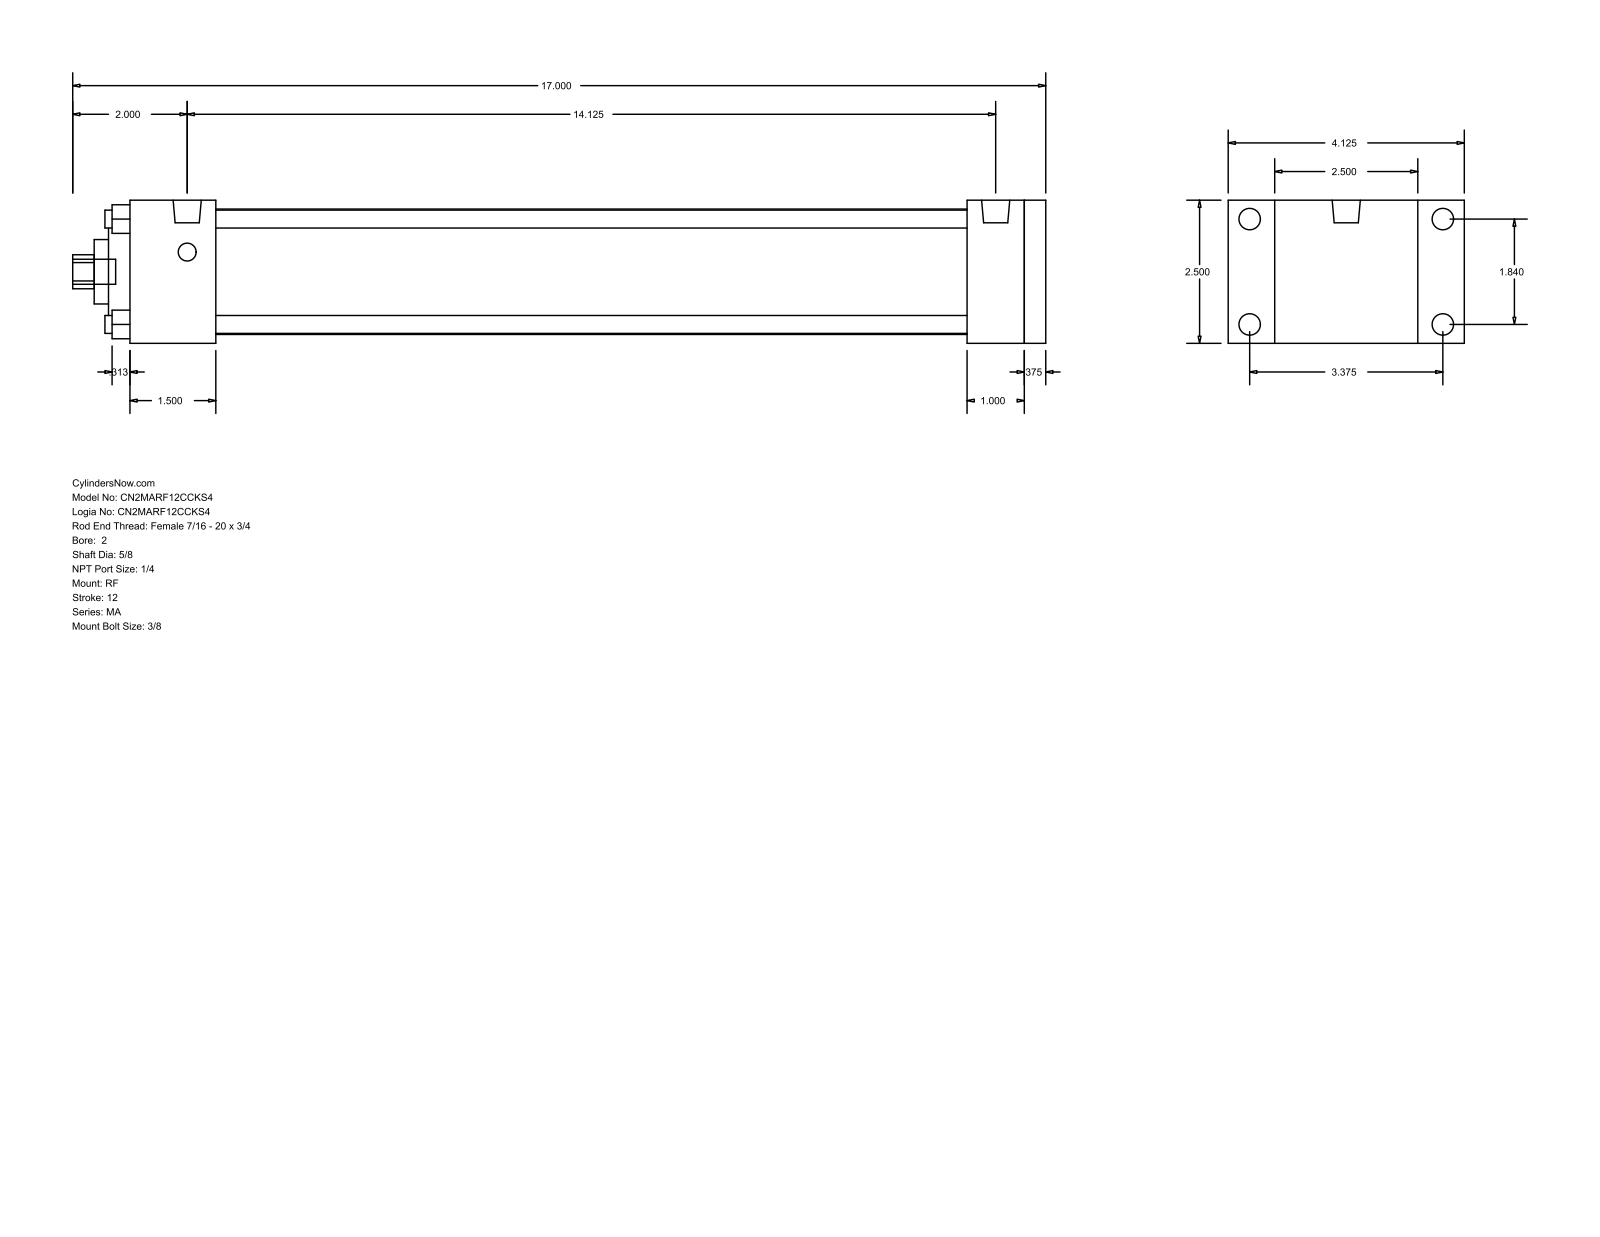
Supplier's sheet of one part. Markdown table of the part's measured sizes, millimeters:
| quantity | value |
| --- | --- |
| part name | MA_RF__0200_0.625 |
| STEP written by | GSSL Pune (CONFIG_CONTROL_DESIGN) |
| units | millimeters |
| bodies | 0 solids, 94 faces (65 planar, 29 cylindrical, 0 other) |
| overall size | 431.8 × 104.78 × 63.5 |
| round holes (diameter × count) | 7.94 × 4, 15.88 × 1, 28.57 × 1, 50.8 × 1, 55.63 × 1 |
| round bosses / shafts (diameter × count) | 9.53 × 4, 7.94 × 4, 12.49 × 2, 11.11 × 1 |
| partial cylindrical surfaces (radius × count) | 7.54 × 1 |
| main face-to-face distances | 63.5, 9.53, 38.1, 9.52, 396.87, 406.4, 415.92, 358.77, 368.3, 371.48 |
| hole center spacings | 33.05, 46.74, 66.1 |
